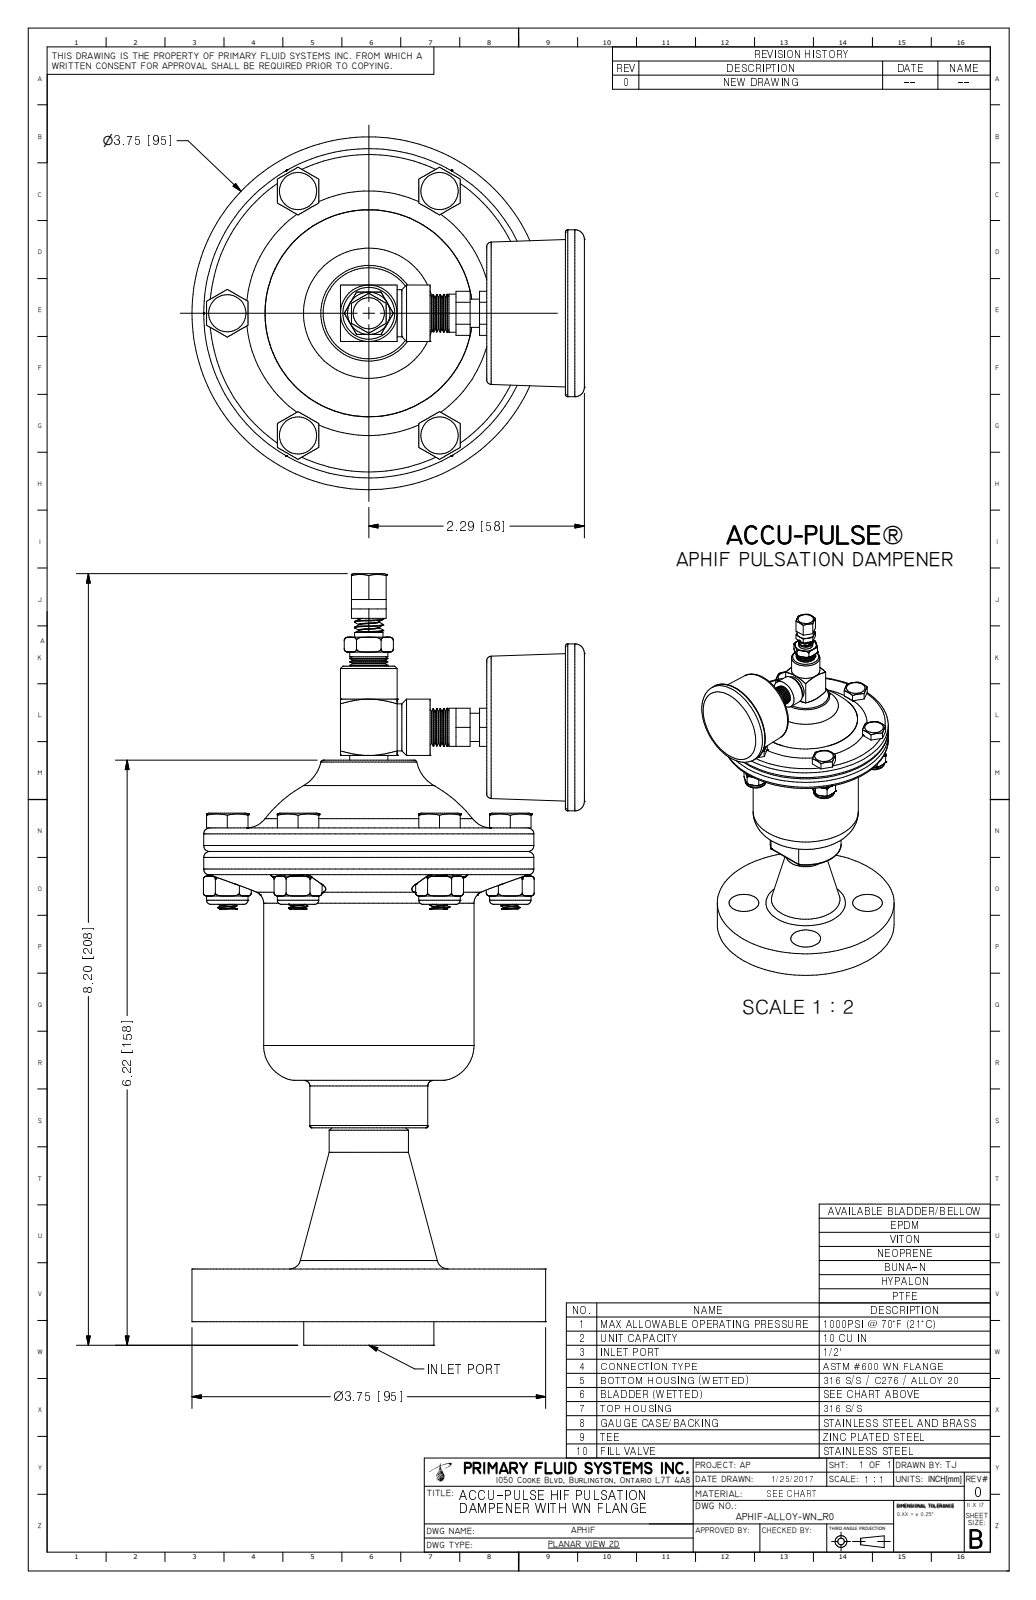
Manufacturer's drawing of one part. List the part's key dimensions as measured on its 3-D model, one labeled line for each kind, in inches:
Part name (STEP PRODUCT): APHIF-ALLOY-WN_R0
STEP written by: Autodesk Inventor 2009 (AUTOMOTIVE_DESIGN)
Units: inches
Bodies: 1 solid, 655 faces (210 planar, 67 cylindrical, 378 other)
Overall size (bounding box): 8.201 × 4.16 × 3.75
Volume: 17.55 in³ · Surface area: 129 in²
Round holes (diameter × count): ⌀0.63 ×4, ⌀0.622 ×1, ⌀1.98 ×1, ⌀2.41 ×1
Round bosses / shafts (diameter × count): ⌀0.44 ×6, ⌀0.144 ×6, ⌀0.6 ×2, ⌀0.405 ×2, ⌀0.3 ×2, ⌀3.75 ×1, ⌀3.5 ×1, ⌀2.23 ×1
Partial cylindrical surfaces — rounded edges, fillets, slot ends (radius × count): R0.02 ×7, R0.238 ×6, R0.025 ×2, R0.06 ×2, R0.75 ×1
Main face-to-face distances: 0.56, 5.248, 4.688, 2.25, 0.75, 1.5, 2.81, 2.438, 1.035, 0.25
Hole centre spacings: 1.31, 1.31, 1.852, 1.853, 2.62
